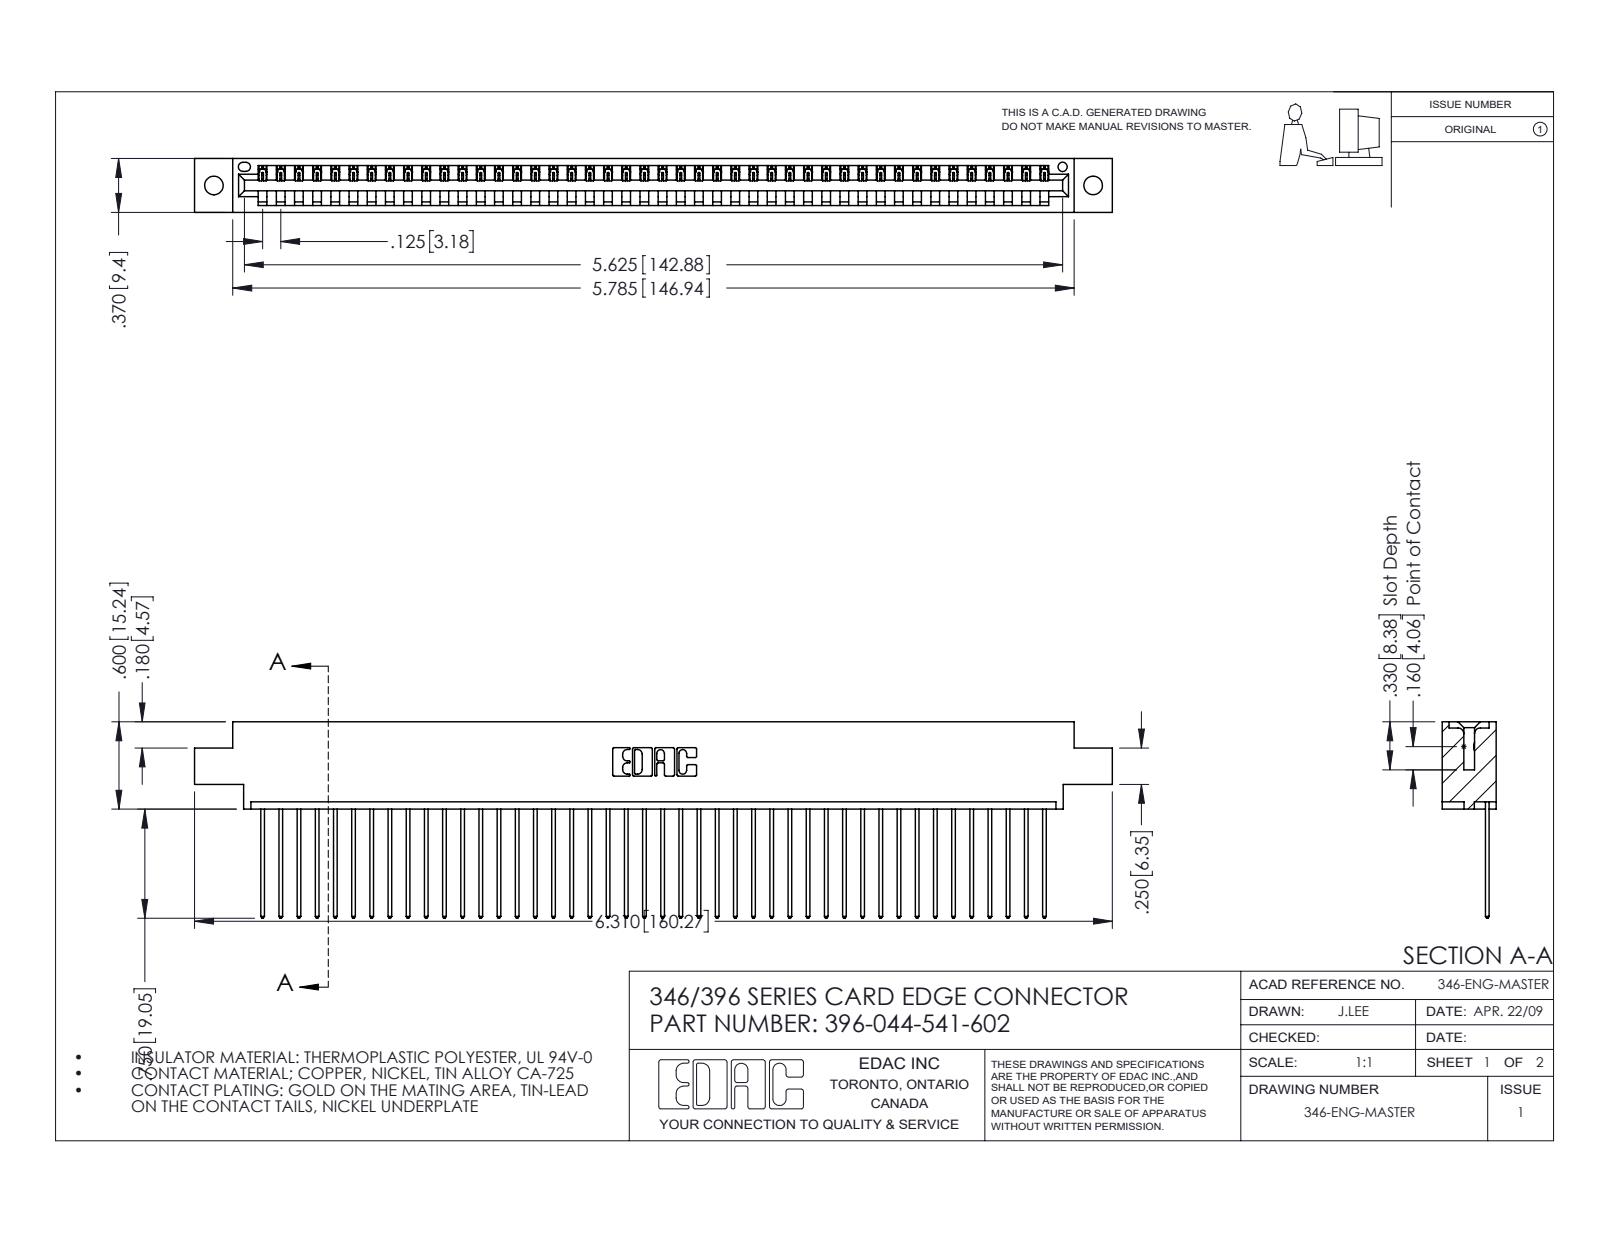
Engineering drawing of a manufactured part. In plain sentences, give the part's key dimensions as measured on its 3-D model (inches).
The part is named "346 Part_0.170 Offset - 0.128 Dia; 396-044-541-602; 345-292-001_345-293-141". Its 3-D file was written by "SolidWorks 2016 (CONFIG_CONTROL_DESIGN)". It is 45 solids with 2678 faces: 1840 planar, 838 cylindrical and 0 other. Overall it measures 6.31 by 1.35 by 0.37 inches. Its volume is 0.934 cubic inches and its surface area 30.86 square inches. Round holes: 2 of diameter 0.128, 1 of diameter 0.064. Partial cylindrical surfaces (rounded edges, fillets, slot ends): 88 of radius 0.006, 88 of radius 0.01, 22 of radius 0.01, 6 of radius 0.007, 6 of radius 0.031, 3 of radius 0.026, 2 of radius 0.031, 2 of radius 0.04. The main face-to-face distances are 0.048, 0.322, 0.37, 0.25, 0.072, 0.298, 0.025, 0.148, 0.222, 0.1. The hole center spacings are 0.246, 5.836, 6.045.
